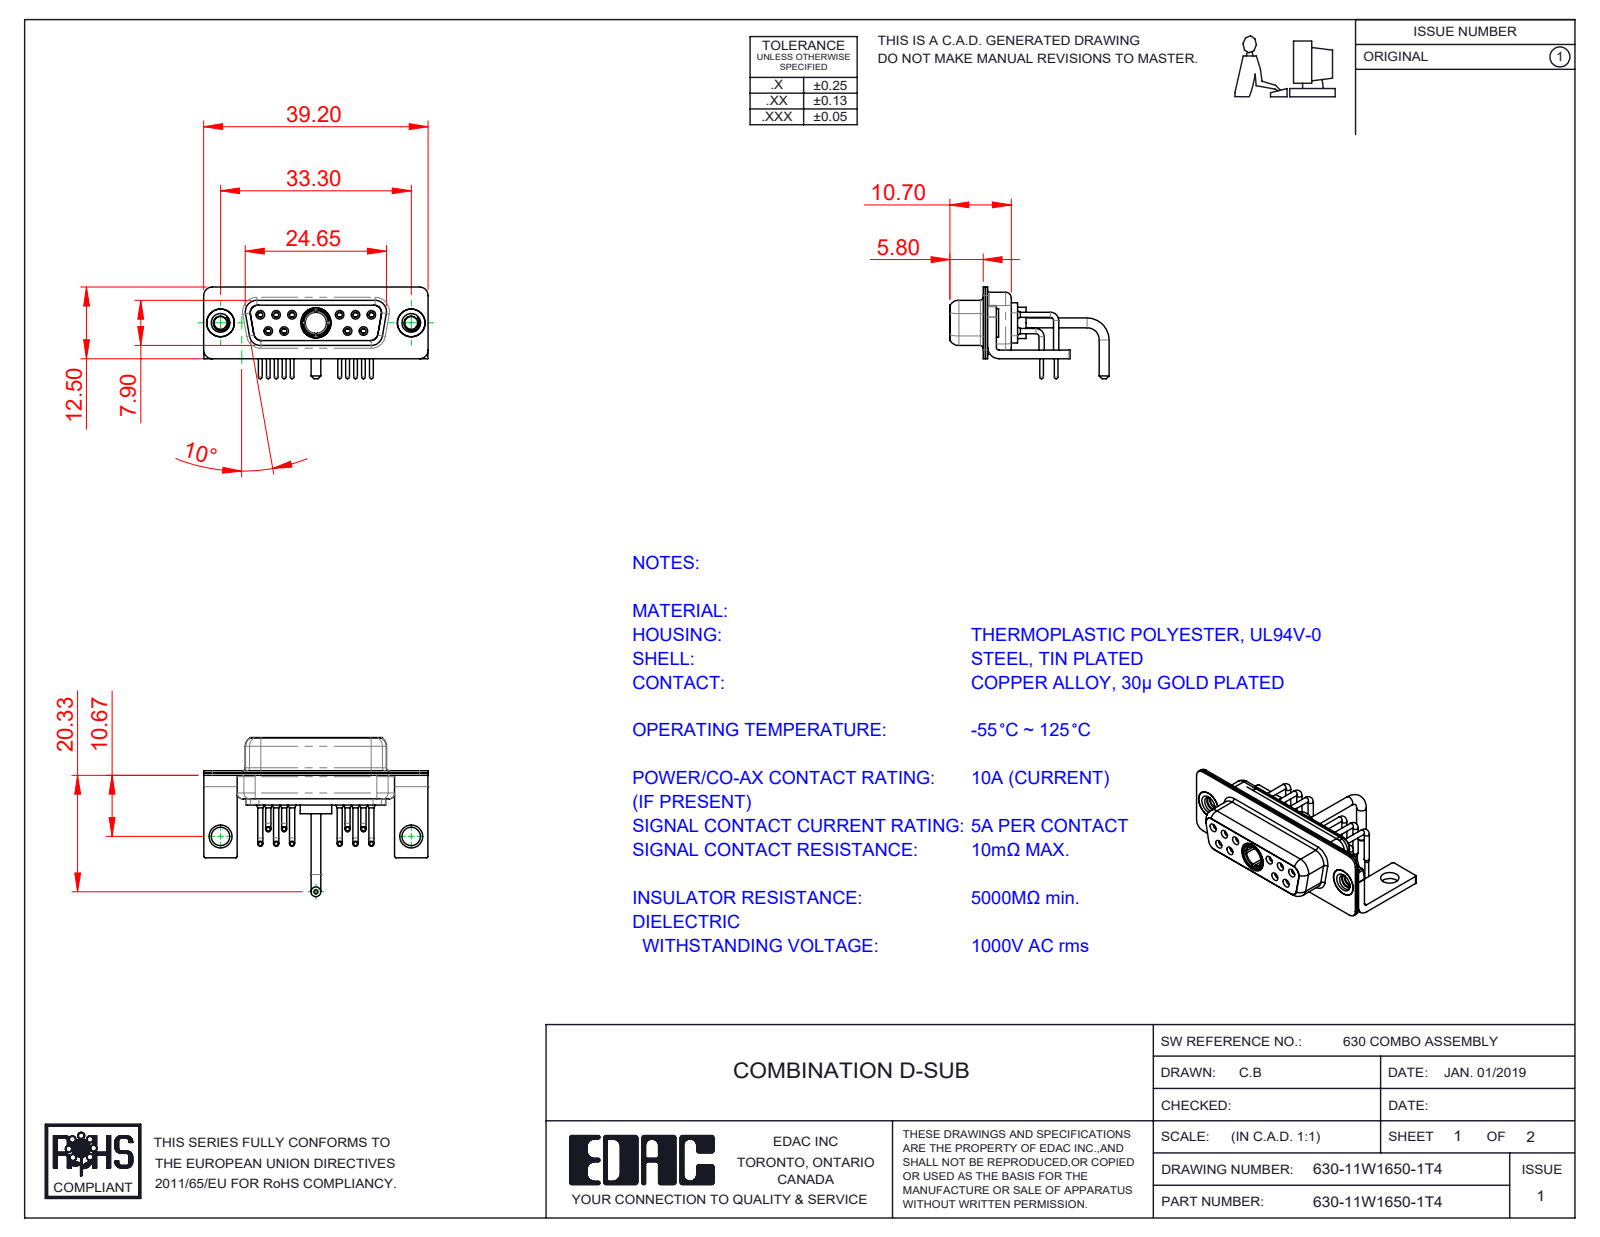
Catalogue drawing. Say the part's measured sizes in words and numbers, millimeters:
The part is named "630Combo Shell Rear_15 Contacts; Power Socket_Ext 10A RA; 630Combo Stabilizer Bracket; 630Combo Housing_11W1 (+5 more)". Its 3-D file was written by "SolidWorks 2020 (CONFIG_CONTROL_DESIGN)". It is 19 solids with 927 faces: 266 planar, 410 cylindrical and 251 other. Overall it measures 39.2 by 27.78 by 16 millimeters. Its volume is 2 872 cubic millimeters and its surface area 6 846 square millimeters. Round holes: 10 of diameter 0.9, 10 of diameter 1.1, 10 of diameter 1.5, 10 of diameter 2, 6 of diameter 1.7, 4 of diameter 1.6, 3 of diameter 4.85, 2 of diameter 2.26, 2 of diameter 3.2, 2 of diameter 4, 2 of diameter 4.05, 1 of diameter 3.7. Round bosses or shafts: 10 of diameter 0.9, 10 of diameter 0.65, 6 of diameter 1.6, 2 of diameter 5, 2 of diameter 4.95, 2 of diameter 4.8, 2 of diameter 1.7, 1 of diameter 5.5. Partial cylindrical surfaces (rounded edges, fillets, slot ends): 16 of radius 0.25, 16 of radius 1.5, 13 of radius 2, 12 of radius 1.35, 8 of radius 1.6, 5 of radius 0.5, 4 of radius 0.6, 4 of radius 0.65. The main face-to-face distances are 0.4, 0.8, 1.4, 0.45, 8.45, 1.5, 1.8, 8.9, 6.2, 2.3. The hole center spacings are 3.16, 2.77, 13.85, 11.08, 16.62, 5.03, 5.04, 5.54.
